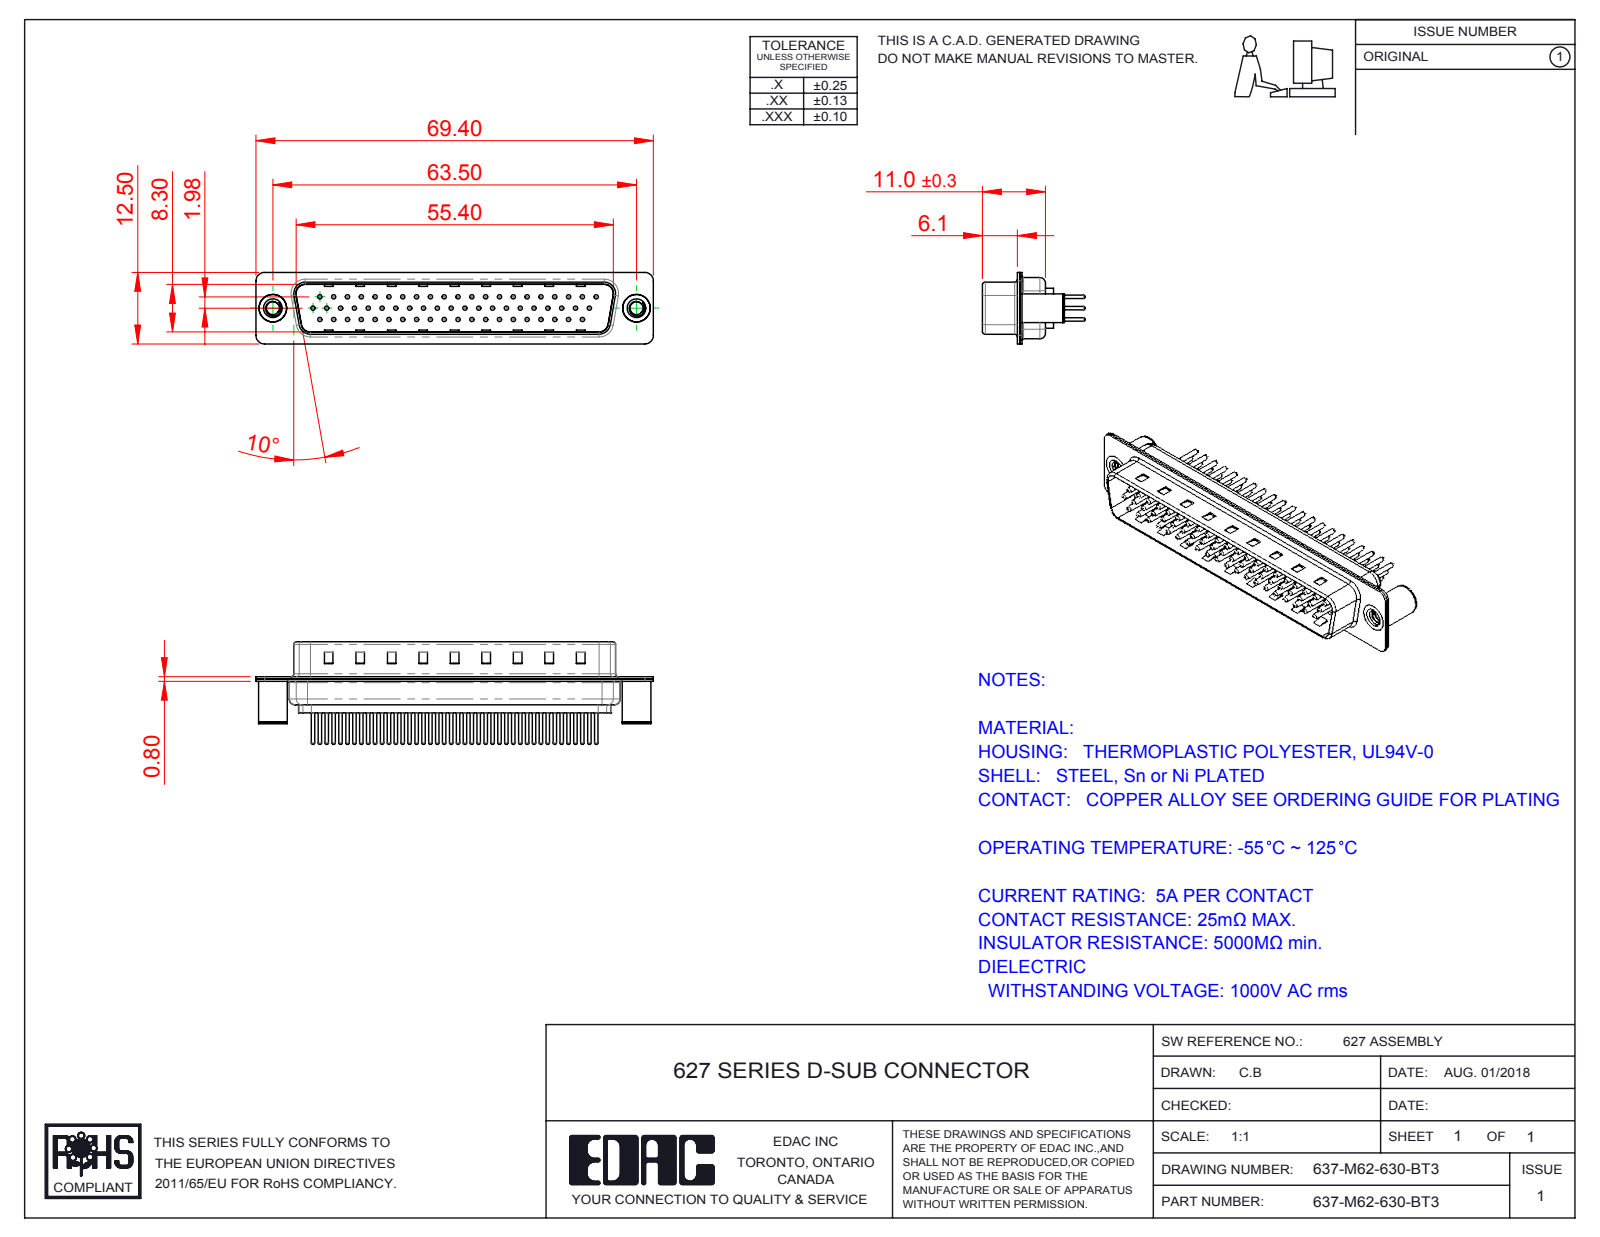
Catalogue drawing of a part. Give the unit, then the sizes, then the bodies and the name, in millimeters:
Units: millimetres
Overall size (bounding box): 69.4 × 17.9 × 12.5
Round holes (diameter × count): ⌀0.75 ×62, ⌀1.6 ×62, ⌀2 ×62, ⌀2.26 ×2, ⌀3.26 ×2, ⌀4 ×2, ⌀4.8 ×2
Round bosses / shafts (diameter × count): ⌀1.5 ×62, ⌀0.6 ×62, ⌀5 ×2, ⌀4.9 ×2
Partial cylindrical surfaces — rounded edges, fillets, slot ends (radius × count): R1.5 ×16, R2 ×12, R0.5 ×8, R1.6 ×8, R0.25 ×4, R0.6 ×4, R0.65 ×4, R0.9 ×4
Main face-to-face distances: 0.4, 0.8, 9.5, 9.1, 8.7, 9.9, 0.75, 0.35, 5.9, 1.2
Hole centre spacings: 7.24, 2.32, 2.41, 4.13, 9.65, 4.83, 14.48, 11.04
Volume: 4 040 mm³ · Surface area: 11 672 mm²
Bodies: 67 solids, 2740 faces (637 planar, 1033 cylindrical, 1070 other)
Part name (STEP PRODUCT): 637M Contact Row 3_30; 637M Contact Row 2_30; 637-M62-630-BT3; 637M Contact Row 1_30 (+4 more)
STEP written by: SolidWorks 2016 (CONFIG_CONTROL_DESIGN)
